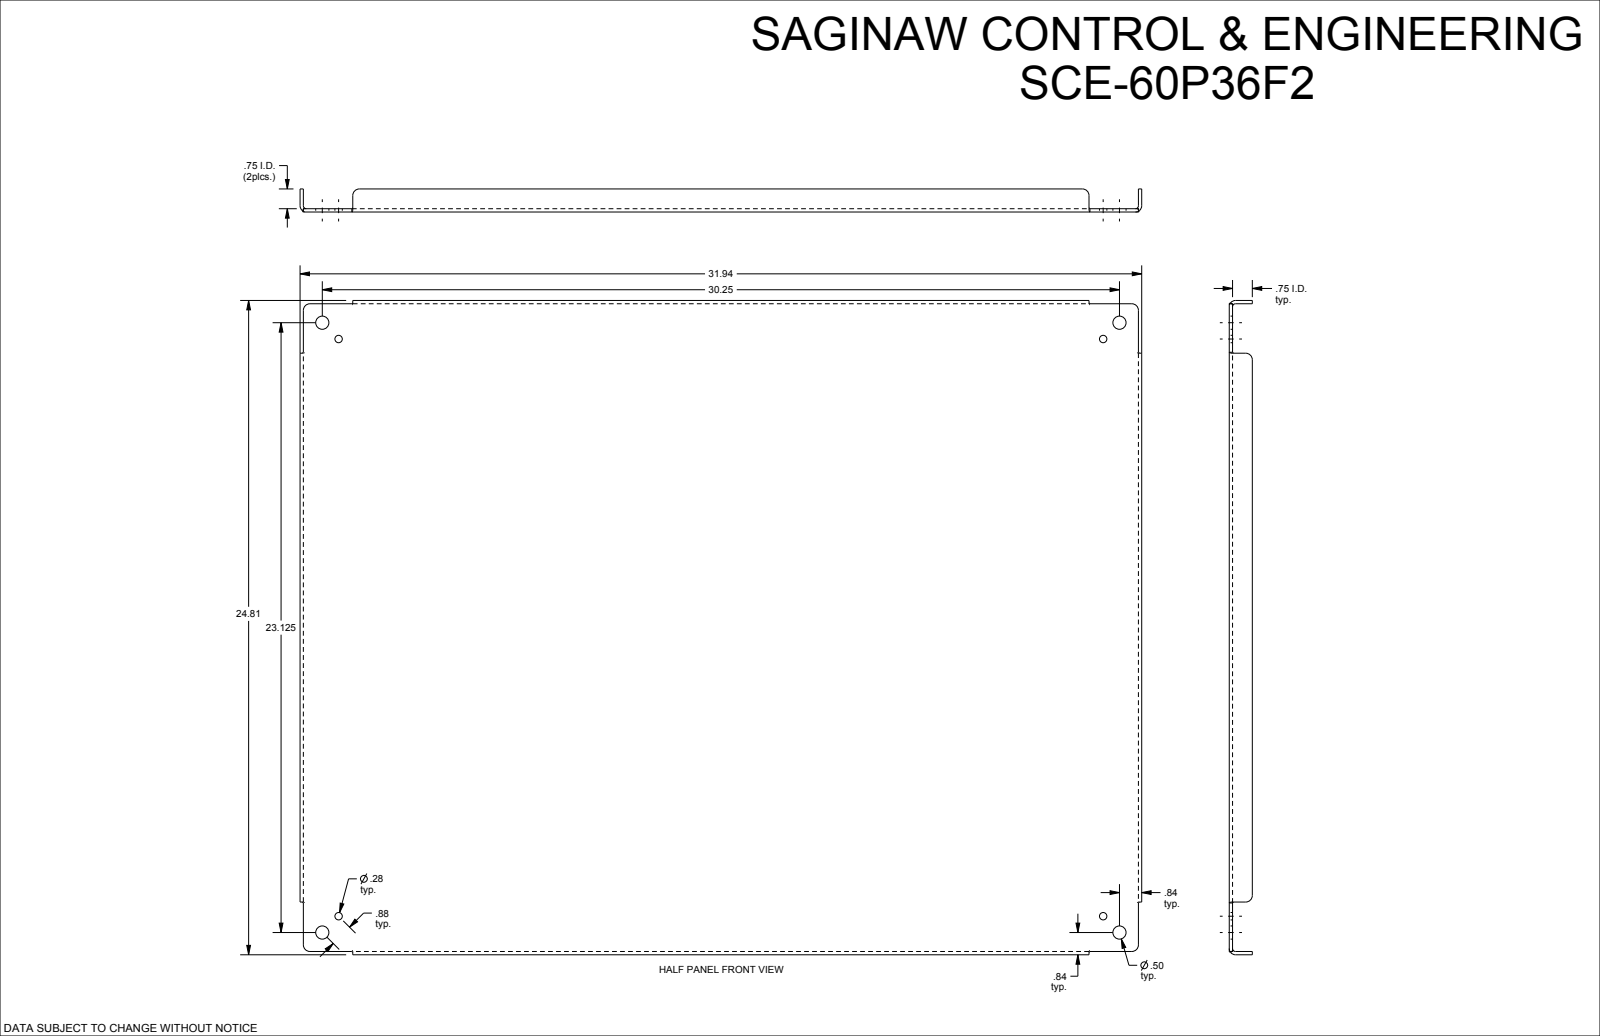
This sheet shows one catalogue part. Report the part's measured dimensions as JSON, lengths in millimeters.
{"part_name": "SCE-60P36F2", "step_written_by": "SolidWorks 2019 (CONFIG_CONTROL_DESIGN)", "units": "millimeters", "bodies": {"solids": 1, "faces": 82, "planar": 30, "cylindrical": 28, "other": 24}, "overall_size": [811.2, 630.3, 22.2], "volume_mm3": 1752000, "surface_area_mm2": 1114000, "round_holes": [[7.1, 4], [12.7, 4]], "partial_cylinders_radius": [[6.4, 8], [2.8, 4], [6, 4]], "face_to_face_distances": [3.2, 3.2, 627, 808.1, 623.9, 630.3, 804.8, 811.2, 19.1, 22.2], "hole_center_spacings": [22.2, 571.9, 752.8, 945.1, 555.9, 587.4, 736.9, 768.4]}
